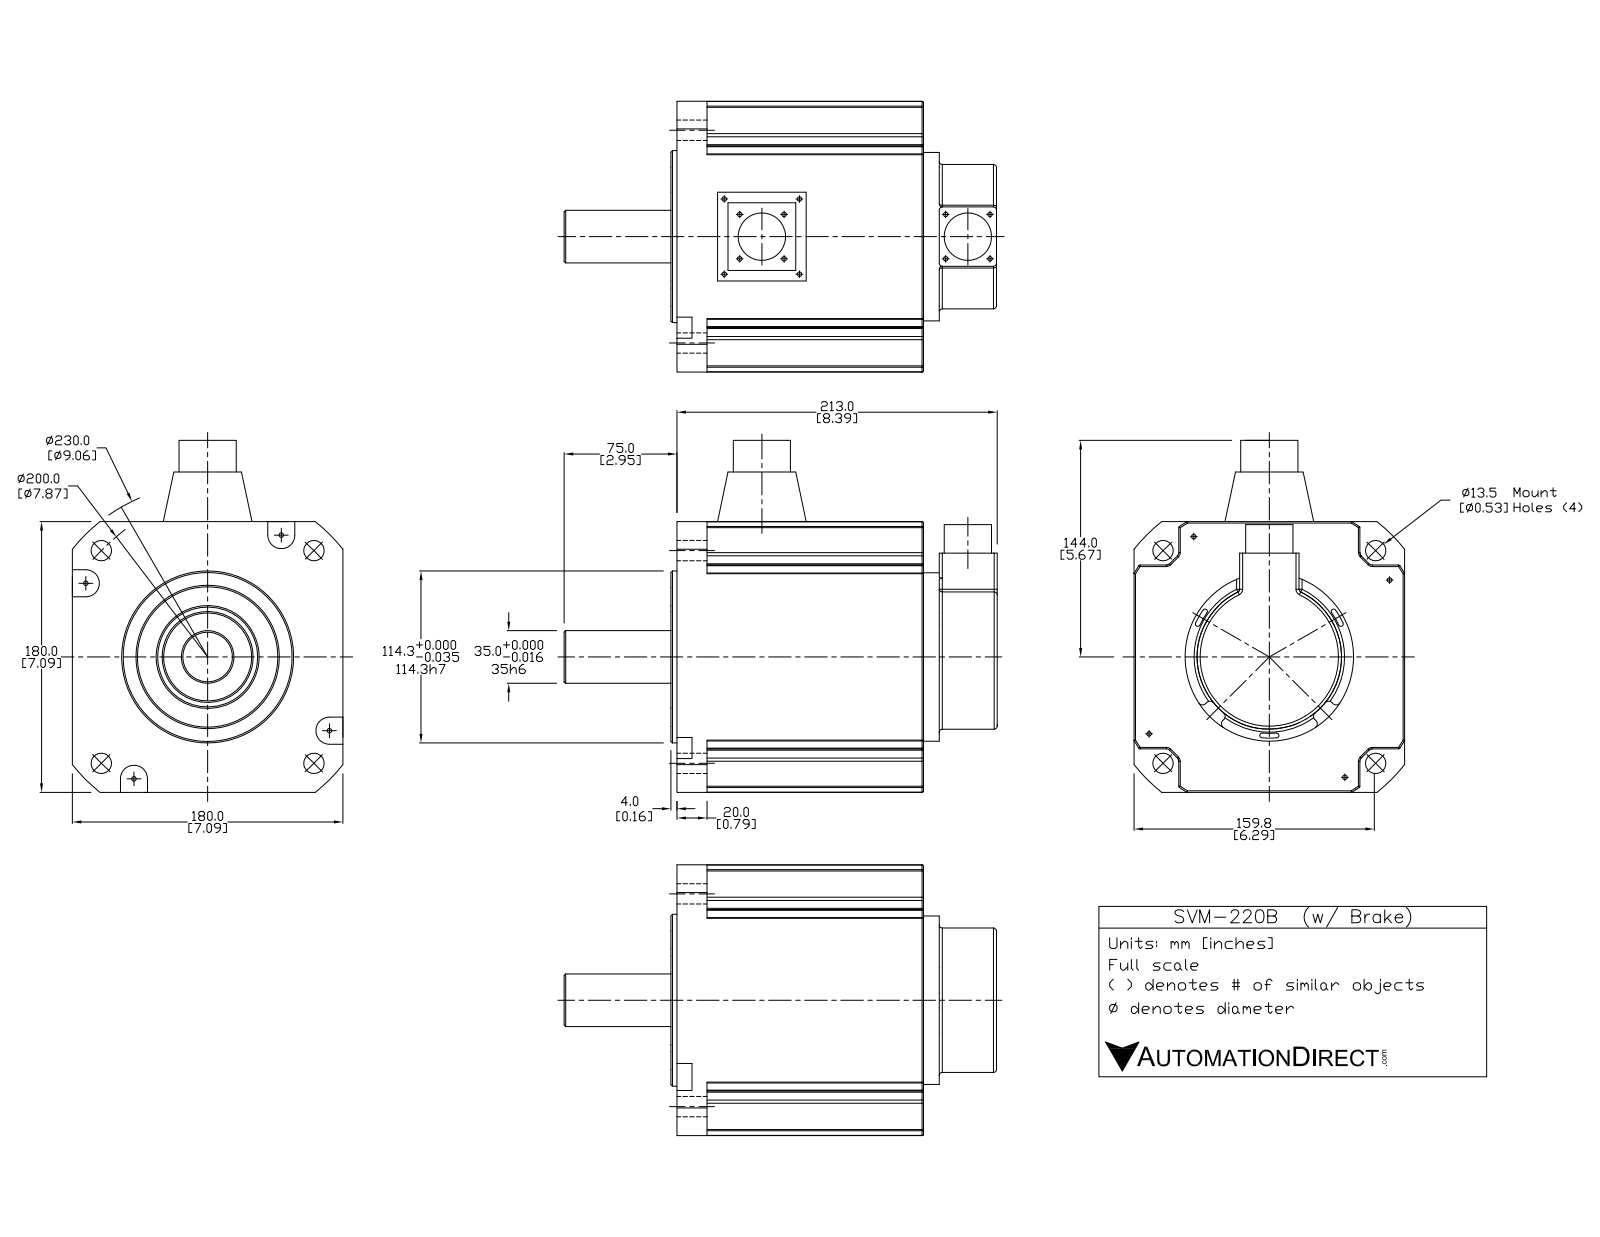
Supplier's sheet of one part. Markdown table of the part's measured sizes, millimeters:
| quantity | value |
| --- | --- |
| part name | SVM-220B |
| STEP written by | SolidWorks 2015 (AUTOMOTIVE_DESIGN) |
| units | millimeters |
| bodies | 32 solids, 460 faces (238 planar, 135 cylindrical, 87 other) |
| overall size | 288 × 234 × 180 |
| volume | 5 333 000 mm³ |
| surface area | 388 196 mm² |
| round holes (diameter × count) | 13.5 × 4, 27 × 1, 33.3 × 1, 94 × 1 |
| round bosses / shafts (diameter × count) | 2 × 17, 2.4 × 6, 16 × 4, 3.6 × 3, 114.25 × 1, 112 × 1, 96 × 1, 67 × 1 |
| partial cylindrical surfaces (radius × count) | 5 × 8, 1 × 4, 4 × 4, 6 × 4, 9 × 4, 65 × 1, 115 × 1 |
| main face-to-face distances | 120, 180, 30.97, 140, 20, 18, 15.48, 158, 138, 15.49 |
| hole center spacings | 100, 141.42, 200, 114.5 |
